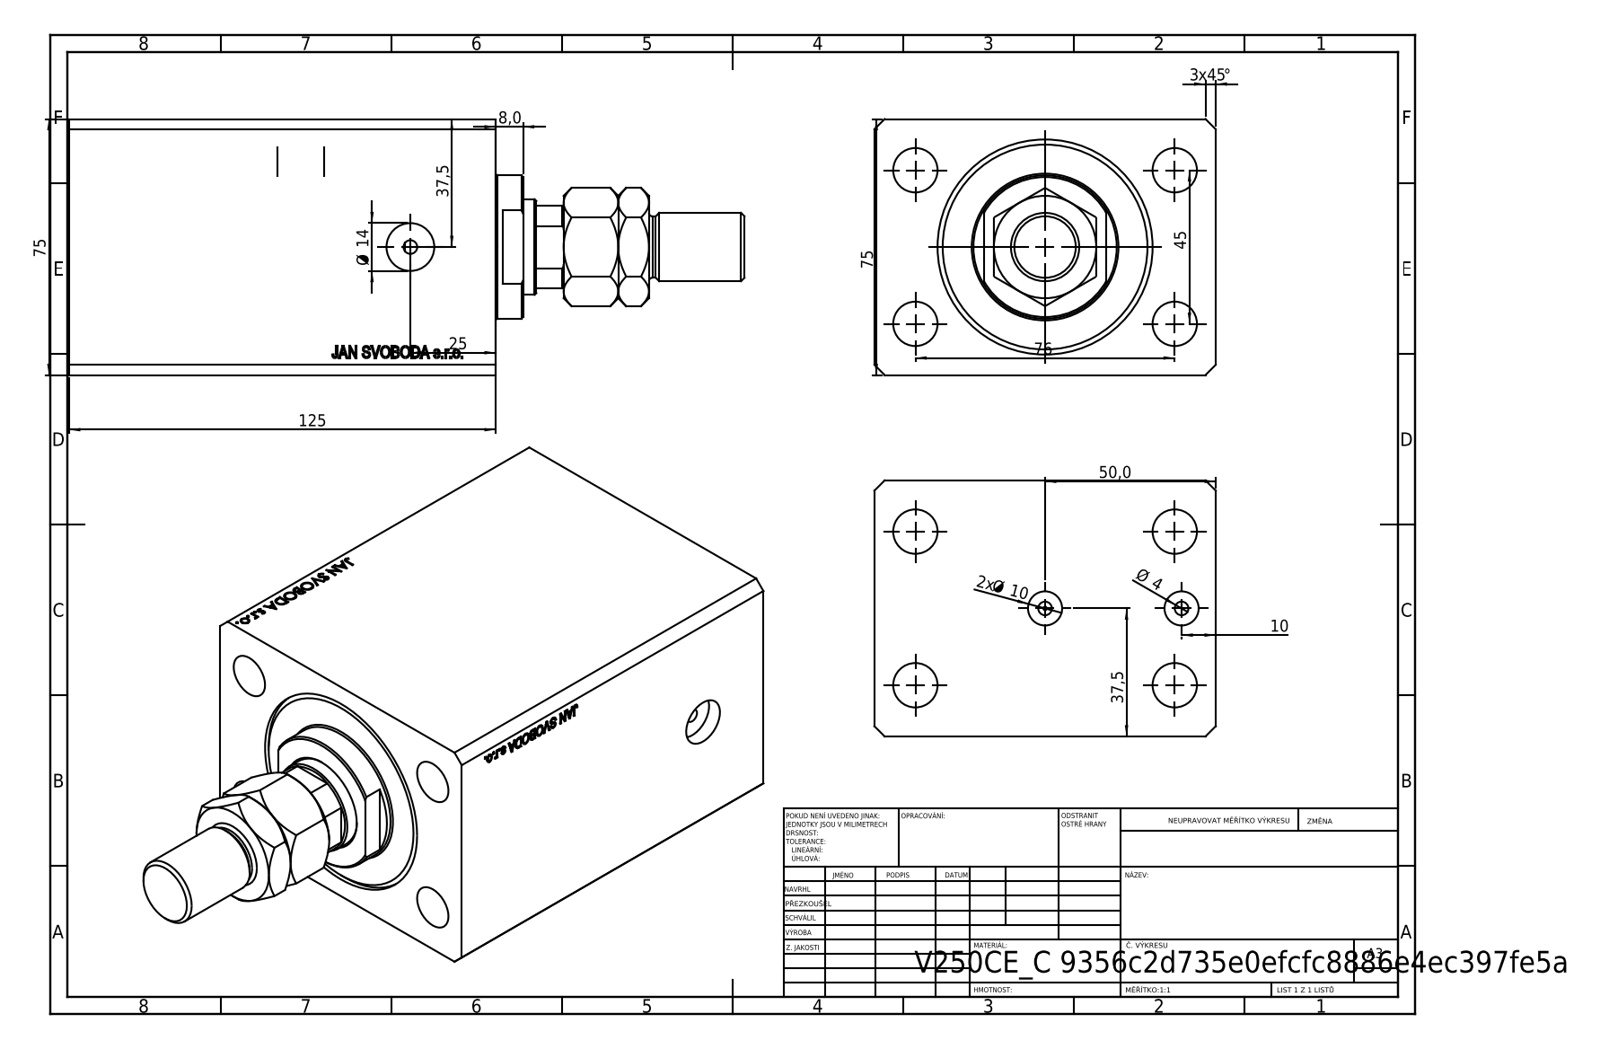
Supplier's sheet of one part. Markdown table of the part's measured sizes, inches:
| quantity | value |
| --- | --- |
| part name | MTA; V250CE_C_Body; V250CE_C_VCP; V250CE_VC_C |
| STEP written by | SolidWorks 2019 (CONFIG_CONTROL_DESIGN) |
| units | inches |
| bodies | 4 solids, 917 faces (443 planar, 50 cylindrical, 424 other) |
| overall size | 7.791 × 3.937 × 2.953 |
| volume | 50.85 in³ |
| surface area | 215.1 in² |
| round holes (diameter × count) | 0.157 × 4, 0.512 × 4, 0.394 × 2, 0.551 × 2, 0.049 × 1, 0.728 × 1, 1.102 × 1, 1.969 × 1, 2.48 × 1 |
| round bosses / shafts (diameter × count) | 1.654 × 1, 0.787 × 1, 0.709 × 1 |
| partial cylindrical surfaces (radius × count) | 0.531 × 1 |
| main face-to-face distances | 2.953, 3.937, 4.921, 0.469, 4.453, 3.406, 3.874, 1.047, 5.236, 1.906 |
| hole center spacings | 1.739, 0.889, 1.772, 2.992, 3.196, 3.477, 1.575, 2.953 |
